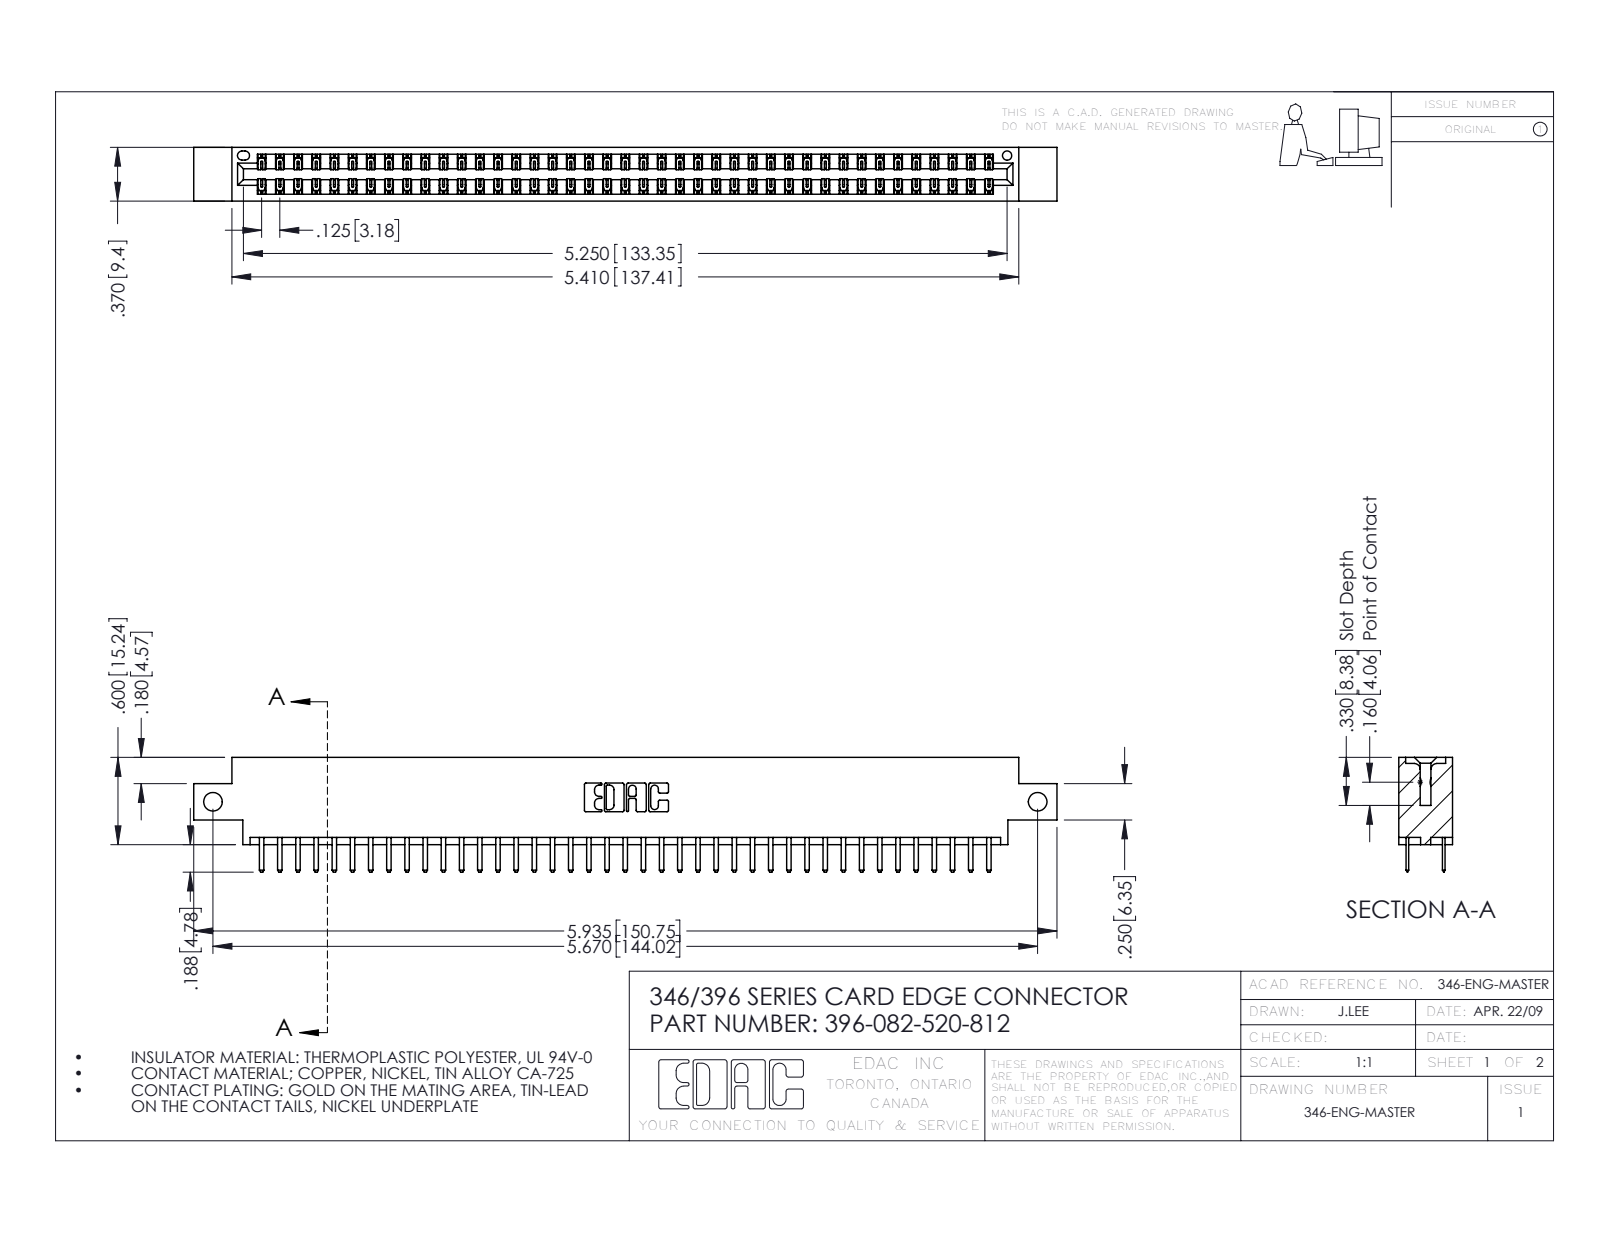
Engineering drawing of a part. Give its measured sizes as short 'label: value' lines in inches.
name: 346 Part_0.170 Offset - Side Mount; 345-292-001_345-293-120; 396-082-520-812
written by: SolidWorks 2016 (CONFIG_CONTROL_DESIGN)
unit: in
bodies: 83 solids, 4718 faces (3114 planar, 1604 cylindrical, 0 other)
size: 5.935 × 0.788 × 0.37
volume: 0.88 in³; area: 30.62 in²
holes: 2× ⌀0.128, 1× ⌀0.064
rounds: 123× R0.006, 86× R0.01, 22× R0.01, 6× R0.007, 6× R0.031, 3× R0.026, 2× R0.014, 2× R0.022
face distances: 0.048, 0.322, 0.25, 0.37, 0.275, 0.072, 0.298, 0.025, 0.148, 0.222
hole spacings: 5.67
